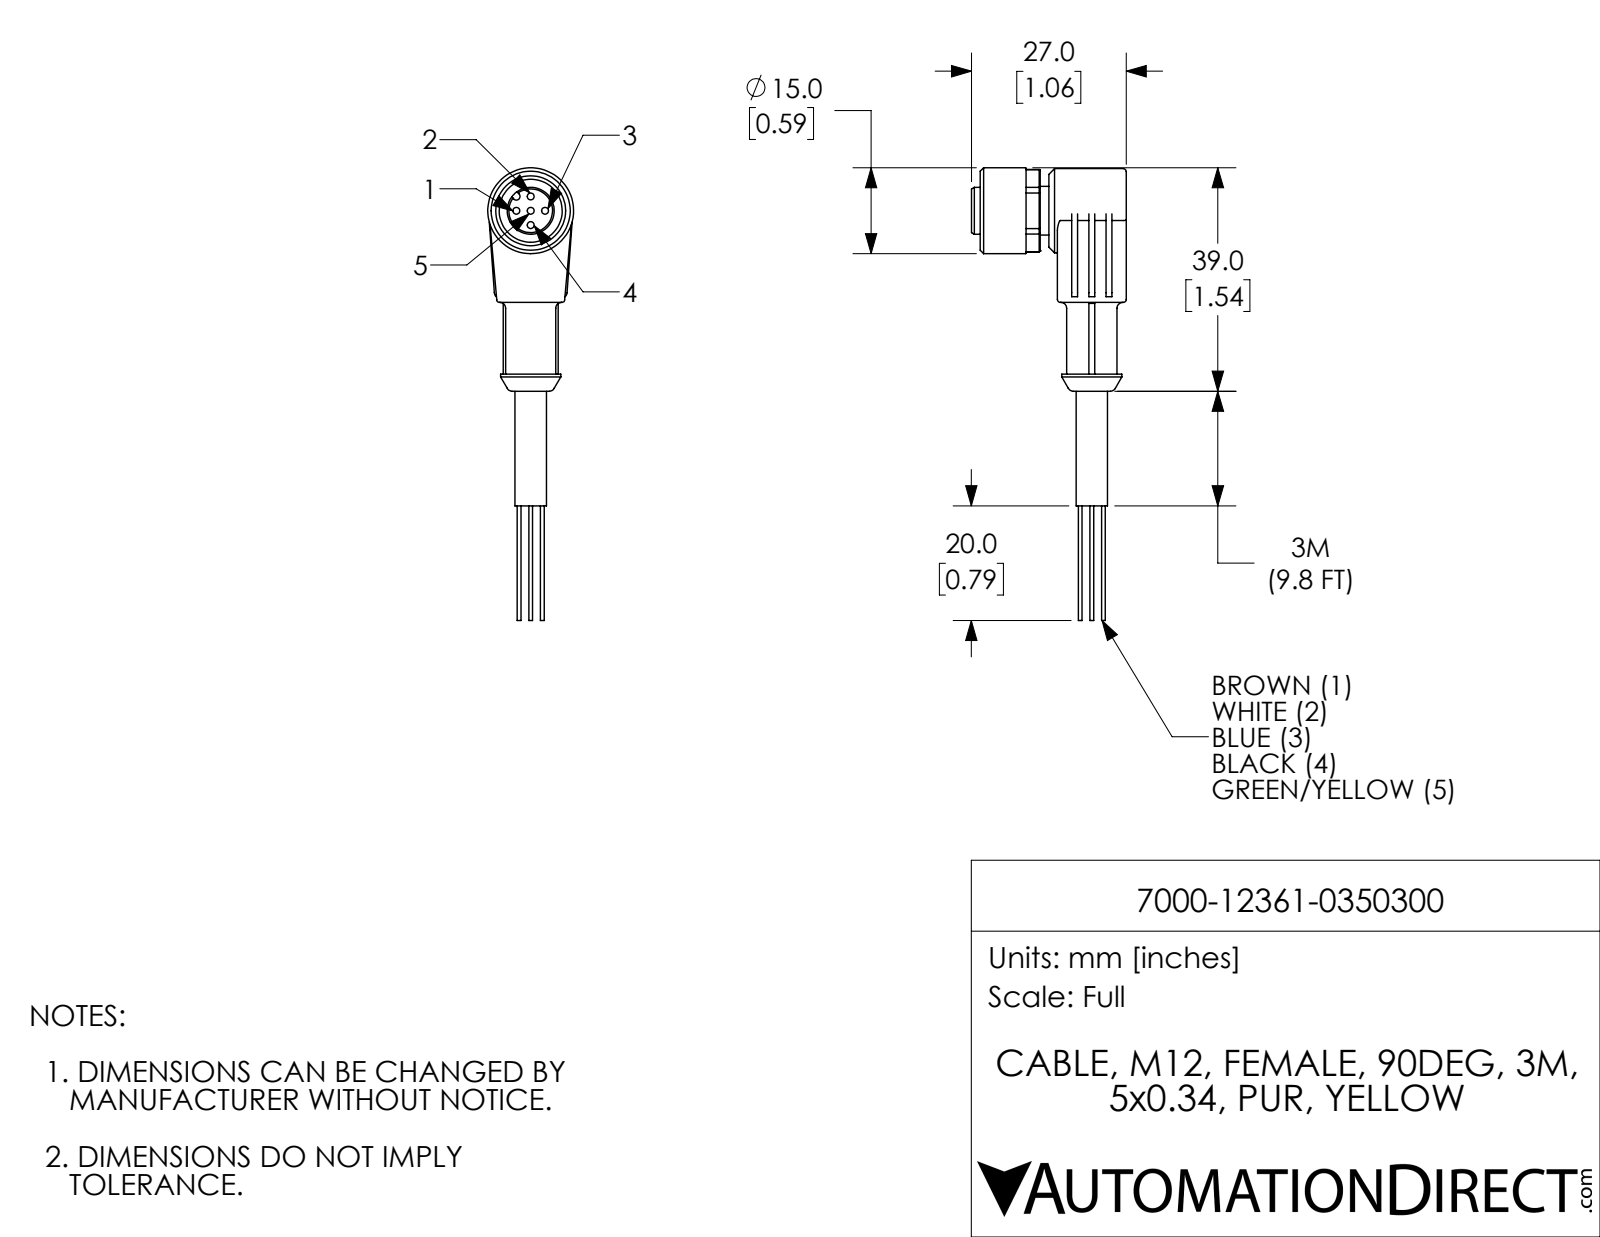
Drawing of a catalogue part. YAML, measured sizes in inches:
part_name: "7000-12361-0350300"
step_written_by: "SolidWorks 2021 (CONFIG_CONTROL_DESIGN)"
units: inches
bodies: {solids: 1, faces: 155, planar: 66, cylindrical: 61, other: 28}
overall_size: [3.11, 1.063, 0.591]
volume: 0.417
surface_area: 5.916
round_holes:
  - {diameter: 0.047, count: 5}
  - {diameter: 0.189, count: 1}
  - {diameter: 0.433, count: 1}
round_bosses_or_shafts:
  - {diameter: 0.026, count: 5}
  - {diameter: 0.591, count: 1}
  - {diameter: 0.579, count: 1}
  - {diameter: 0.413, count: 1}
  - {diameter: 0.346, count: 1}
  - {diameter: 0.335, count: 1}
  - {diameter: 0.323, count: 1}
  - {diameter: 0.217, count: 1}
partial_cylinders:
  - {radius: 0.02, count: 8}
  - {radius: 0.039, count: 2}
  - {radius: 0.026, count: 1}
  - {radius: 0.283, count: 1}
face_to_face_distances: [0.472, 0.059, 0.118, 0.531, 0.591, 0.217, 0.374, 0.236, 0.315, 0.492]
hole_center_spacings: [0.098, 0.139, 0.197]
